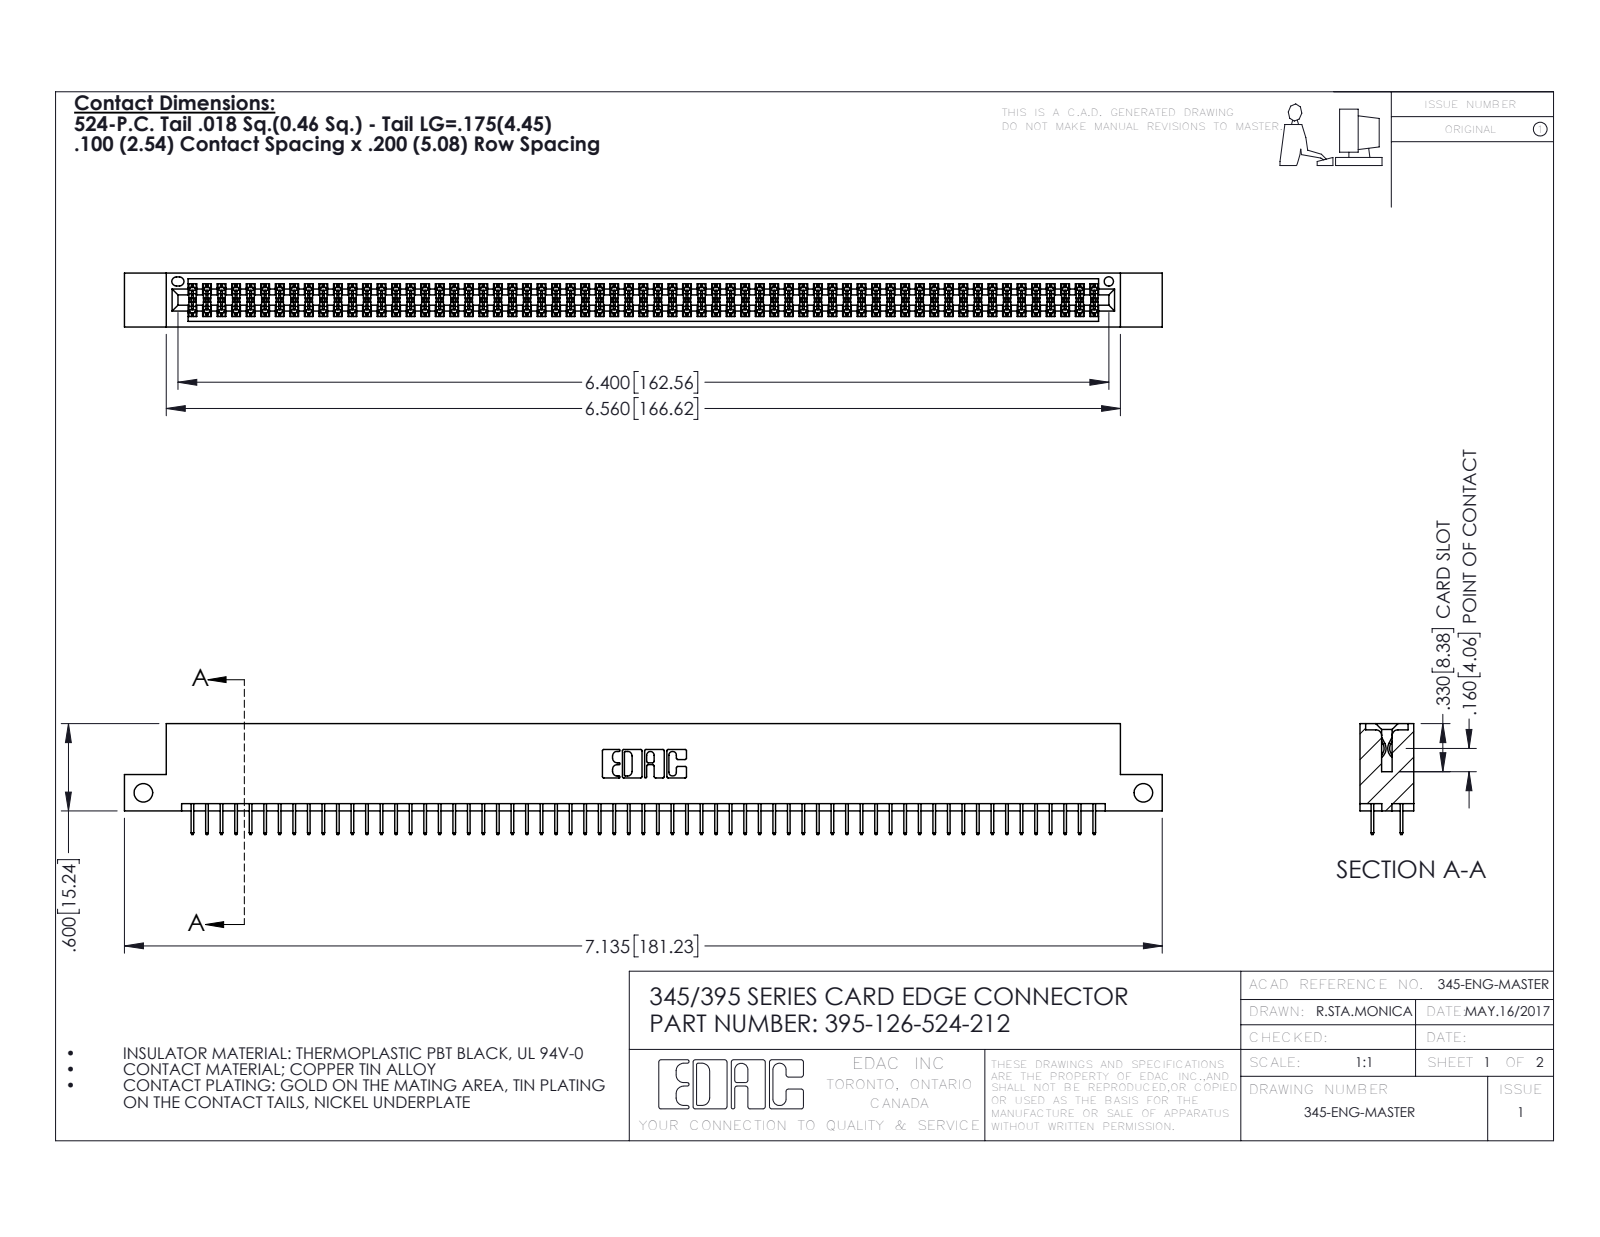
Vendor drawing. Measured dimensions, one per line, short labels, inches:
name: 345 Part_Flush Mounting Lugs - Side Mount; 395-126-524-212; 345-292-001_345-293-124
written by: SolidWorks 2016 (CONFIG_CONTROL_DESIGN)
unit: in
bodies: 127 solids, 6930 faces (4994 planar, 1936 cylindrical, 0 other)
size: 7.135 × 0.762 × 0.37
volume: 1.069 in³; area: 39.79 in²
holes: 2× ⌀0.128, 1× ⌀0.064
rounds: 189× R0.006, 22× R0.01, 6× R0.007, 6× R0.031, 3× R0.026, 2× R0.014, 2× R0.019, 2× R0.022
face distances: 0.072, 0.298, 0.2, 0.37, 0.098, 0.272, 0.025, 0.225, 0.072, 0.175
hole spacings: 6.875
